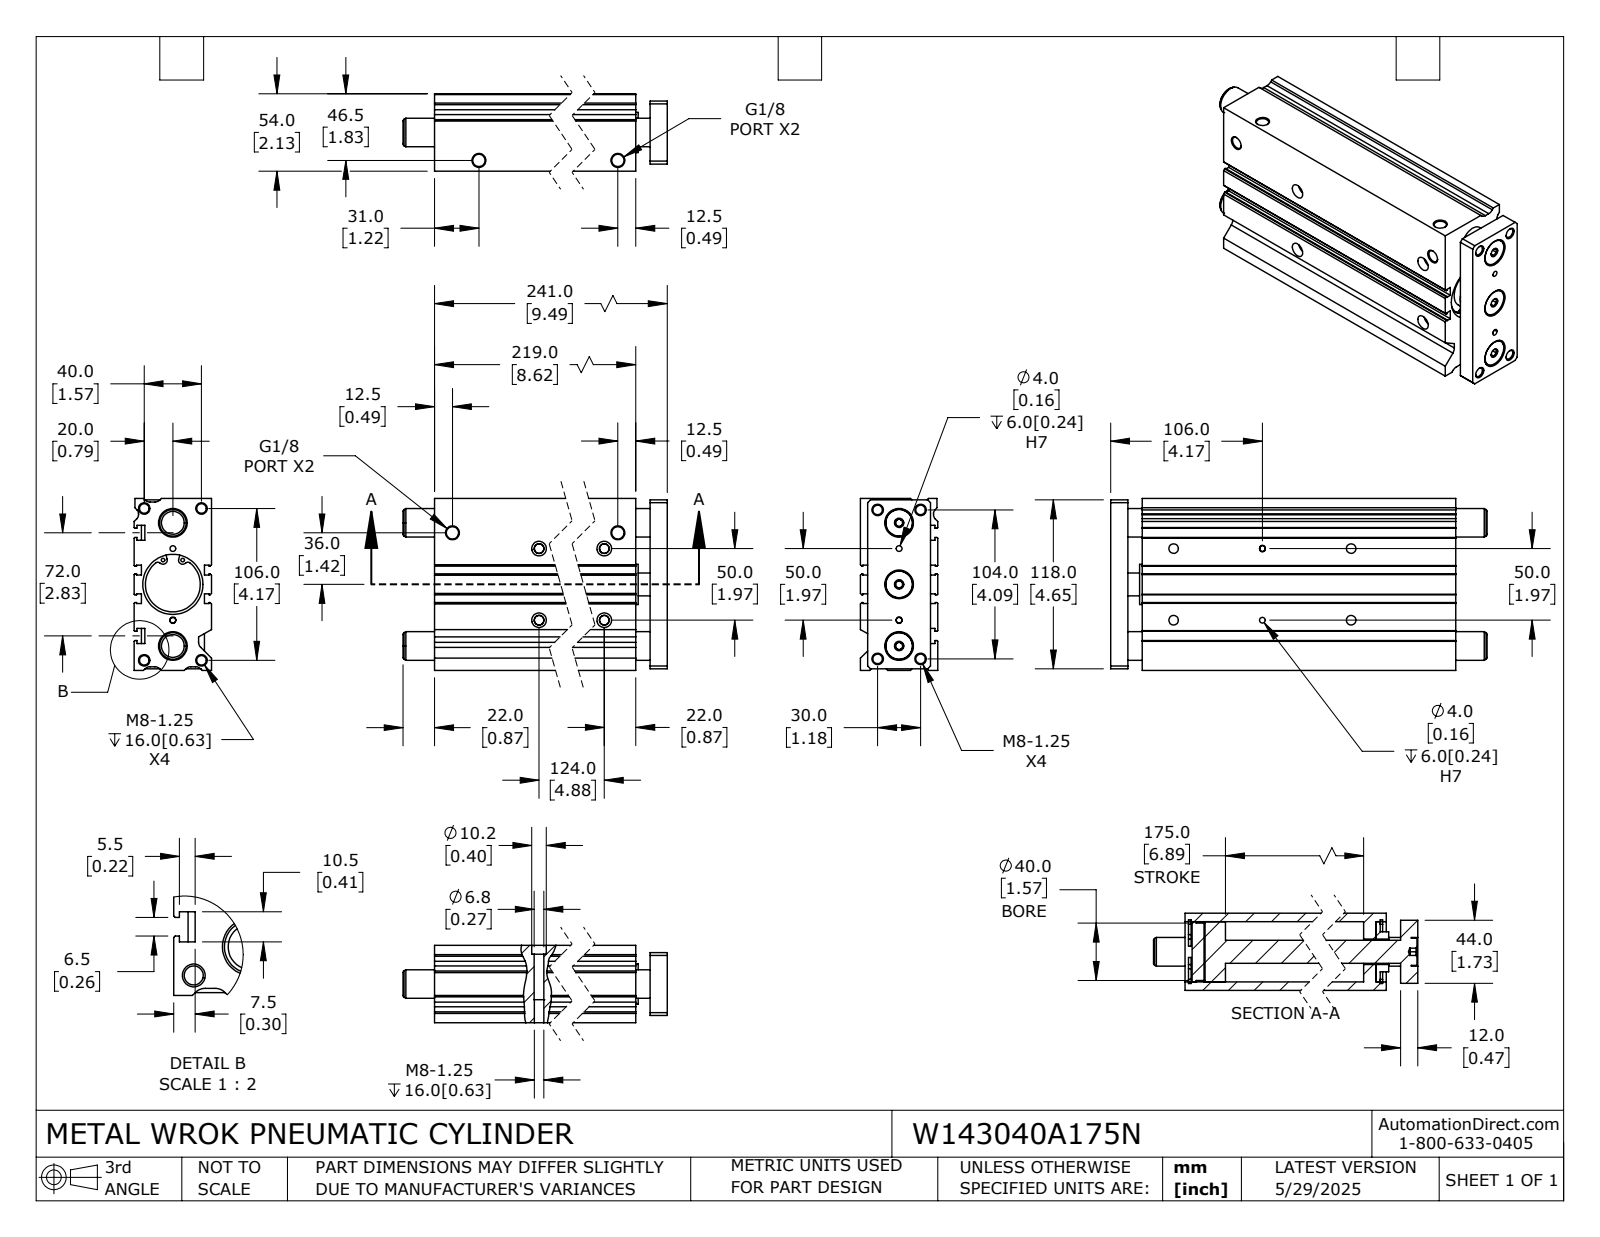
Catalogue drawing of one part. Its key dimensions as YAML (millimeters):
part_name: "W143040A175N; W143040A175N_ROD; W143040A175N_BODY"
step_written_by: "SolidWorks 2024 (CONFIG_CONTROL_DESIGN)"
units: millimeters
bodies: {solids: 6, faces: 393, planar: 192, cylindrical: 151, other: 50}
overall_size: [263, 120, 54]
volume: 1166000
surface_area: 245700
round_holes:
  - {diameter: 6.7, count: 12}
  - {diameter: 2.5, count: 4}
  - {diameter: 4, count: 4}
  - {diameter: 6.8, count: 4}
  - {diameter: 8.6, count: 4}
  - {diameter: 10.2, count: 4}
  - {diameter: 5, count: 3}
  - {diameter: 20, count: 3}
  - {diameter: 17.7, count: 1}
  - {diameter: 38.4, count: 1}
round_bosses_or_shafts:
  - {diameter: 19, count: 3}
  - {diameter: 44.5, count: 2}
  - {diameter: 42, count: 1}
  - {diameter: 40, count: 1}
  - {diameter: 28, count: 1}
  - {diameter: 16, count: 1}
partial_cylinders:
  - {radius: 5, count: 7}
  - {radius: 2, count: 4}
  - {radius: 2.3, count: 4}
  - {radius: 2.9, count: 4}
  - {radius: 4, count: 2}
face_to_face_distances: [54, 5, 49, 2.5, 120, 7.5, 46.5, 22, 41.5, 44]
hole_center_spacings: [5.1, 10.5, 17.5, 18.3, 22.4, 26.9, 30.9, 34.4]
